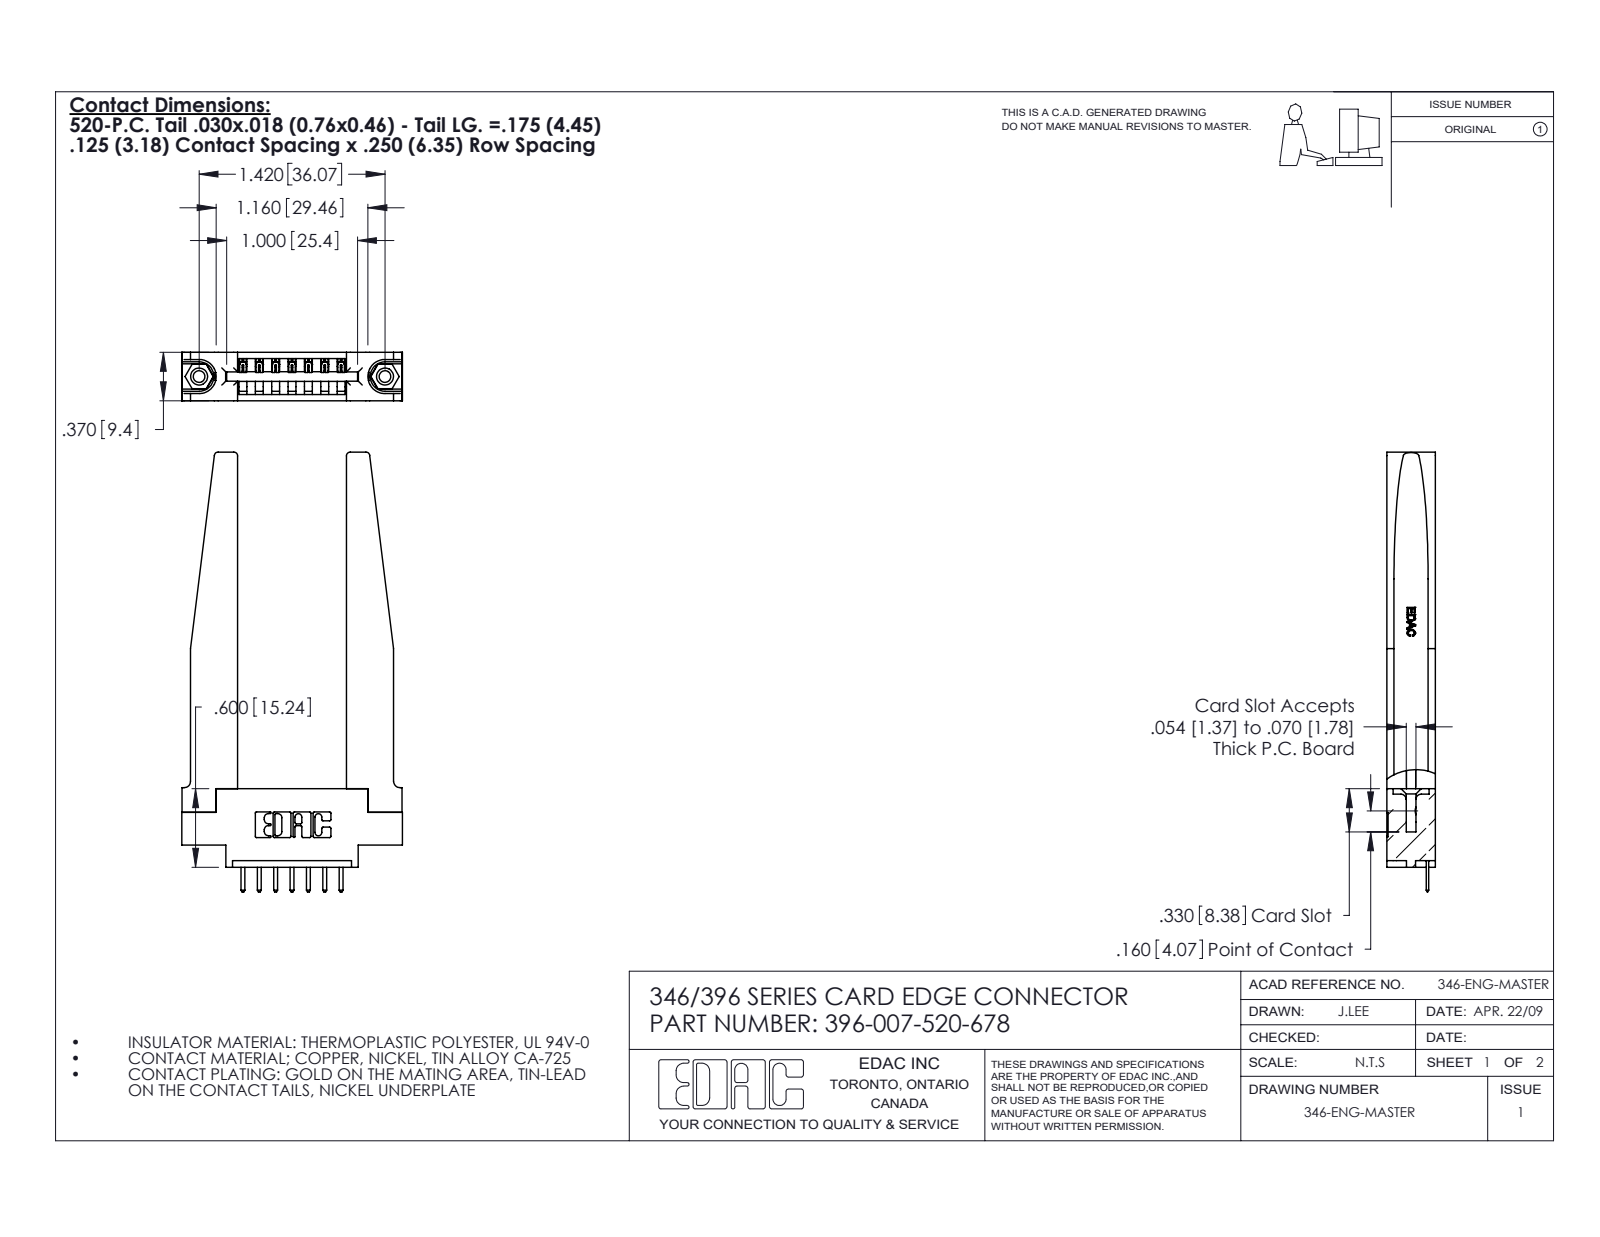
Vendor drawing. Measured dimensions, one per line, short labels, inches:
name: 346 Part_0.170 Offset - 0.156 Dia-TH; 396-007-520-678; 345-292-001_345-293-120; 346-220-078_345-220-078 (+1 more)
written by: SolidWorks 2020 (CONFIG_CONTROL_DESIGN)
unit: in
bodies: 12 solids, 808 faces (530 planar, 226 cylindrical, 52 other)
size: 3.358 × 1.685 × 0.37
volume: 0.645 in³; area: 16.84 in²
holes: 2× ⌀0.089, 2× ⌀0.125, 2× ⌀0.156, 1× ⌀0.064
bosses: 2× ⌀0.155
rounds: 22× R0.01, 16× R0.01, 14× R0.006, 8× R0.03, 6× R0.007, 6× R0.031, 3× R0.026, 2× R0.031
face distances: 0.37, 0.15, 0.22, 0.831, 0.25, 0.072, 0.148, 0.102, 0.048, 0.322
hole spacings: 0.246, 1.217, 1.42
